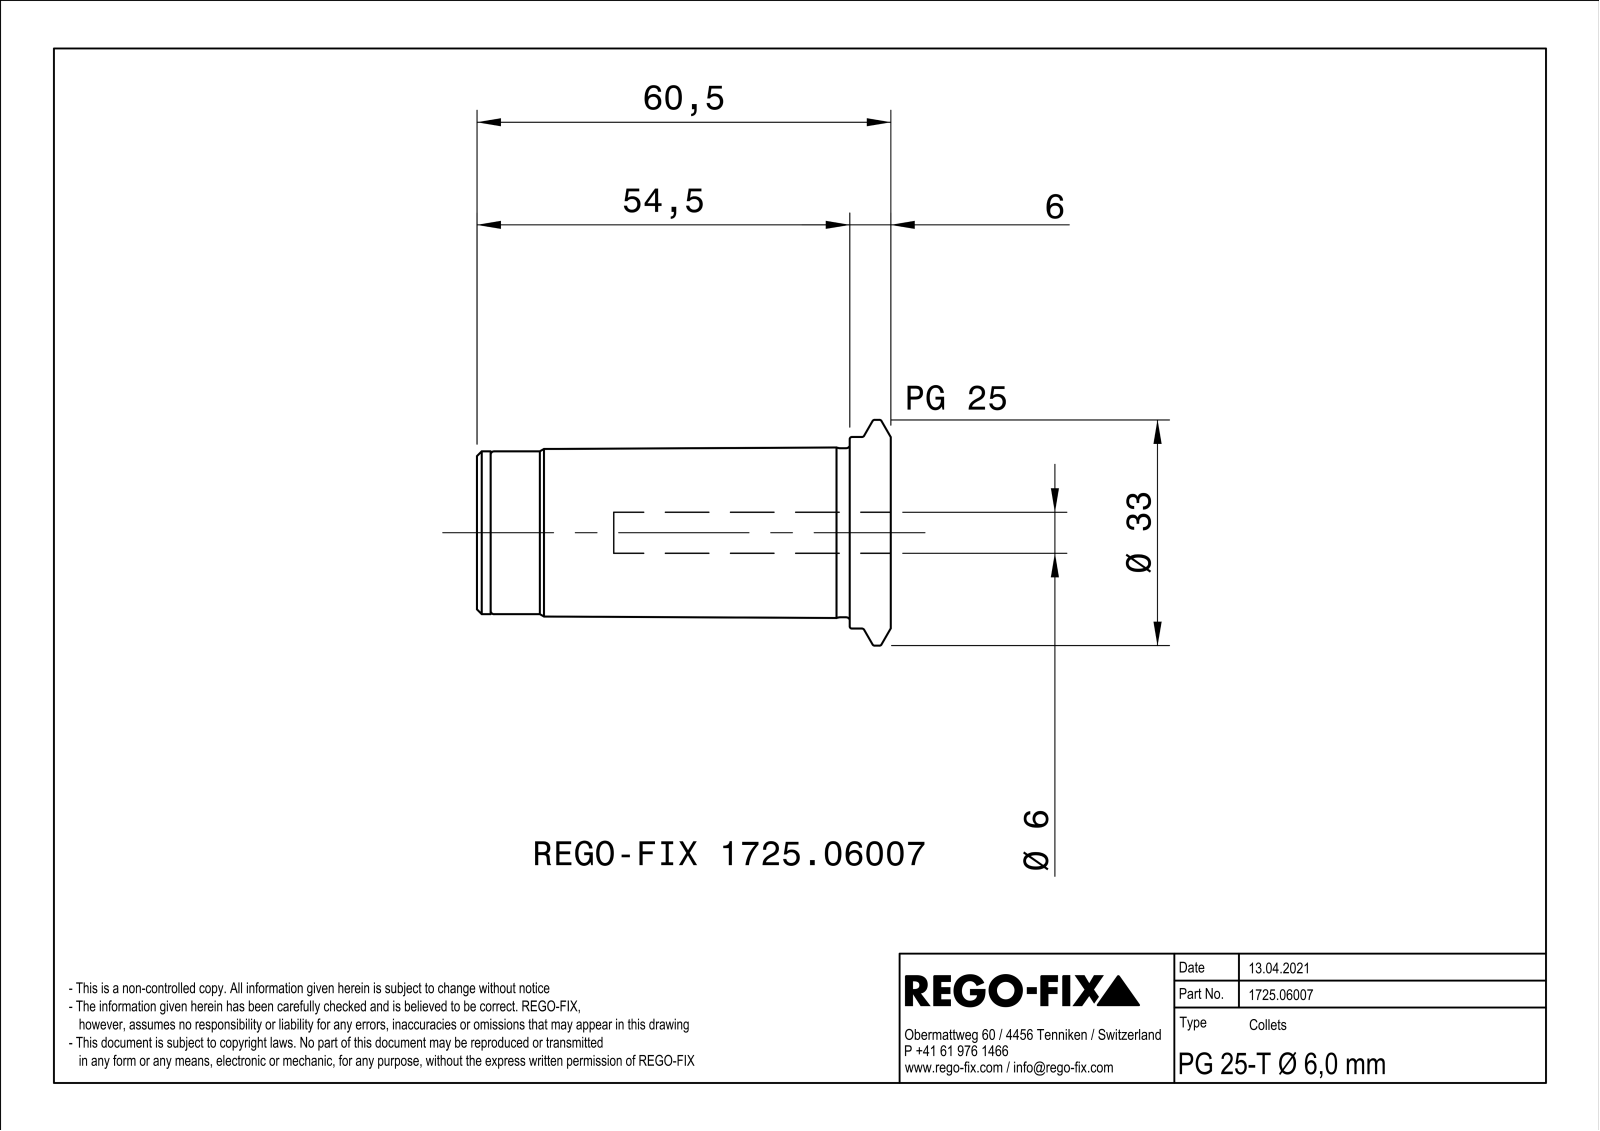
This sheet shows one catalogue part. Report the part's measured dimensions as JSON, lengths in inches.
{"part_name": "NOCUT", "step_written_by": "SIEMENS PLM Software Solid Edge ST10 (AUTOMOTIVE_DESIGN)", "units": "inches", "bodies": {"solids": 0, "faces": 88, "planar": 24, "cylindrical": 23, "other": 41}, "overall_size": [2.303, 1.299, 1.297], "round_holes": [[0.128, 1], [0.169, 1], [0.236, 1], [0.354, 1], [0.827, 1], [0.866, 1]], "round_bosses_or_shafts": [[1.299, 1], [1.102, 1], [0.972, 1], [0.937, 1]], "partial_cylinders_radius": [[0.02, 2], [0.16, 1], [0.164, 1]], "face_to_face_distances": [0.039, 0.236, 2.201, 2.244, 1.965, 2.008, 0.043, 2.303, 2.067, 0.102]}
